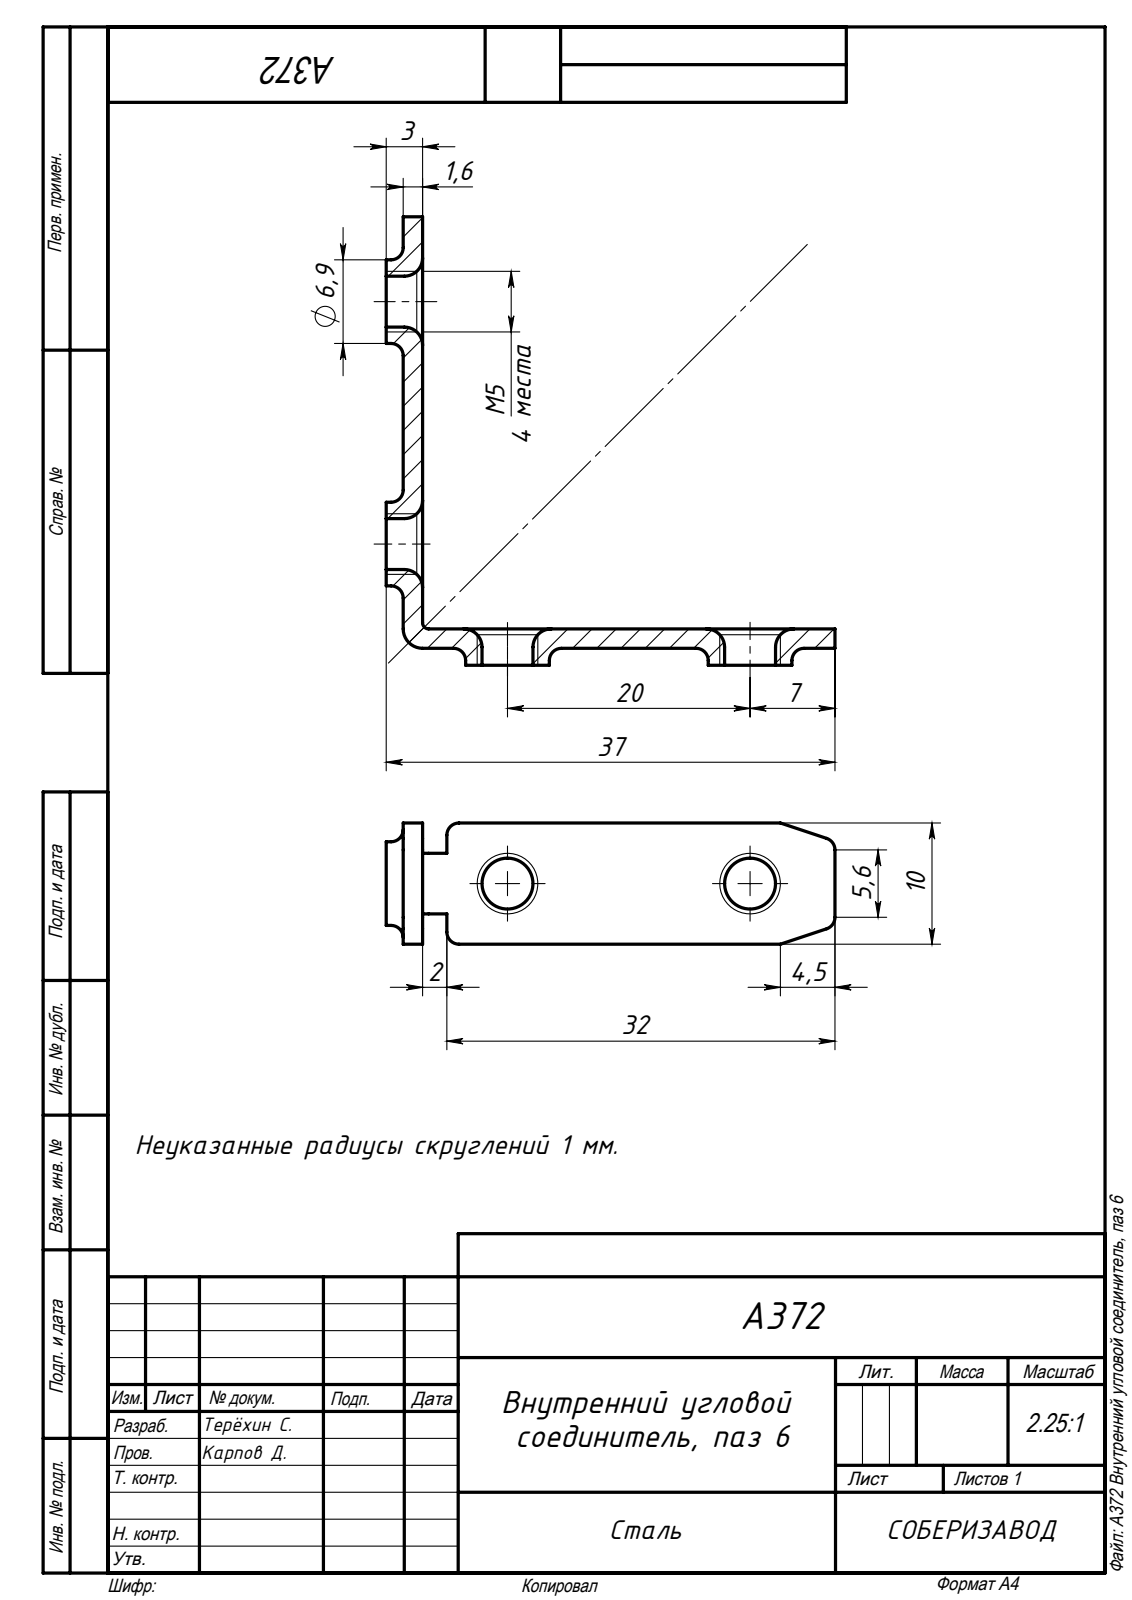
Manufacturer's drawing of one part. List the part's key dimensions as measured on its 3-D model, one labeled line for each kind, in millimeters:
Part name (STEP PRODUCT): A372 Внутренний угловой соединитель, паз 6
STEP written by: SolidWorks 2020 (AUTOMOTIVE_DESIGN)
Units: millimetres
Bodies: 1 solid, 66 faces (24 planar, 26 cylindrical, 16 other)
Overall size (bounding box): 37 × 37 × 10
Volume: 1 076 mm³ · Surface area: 1 663 mm²
Round holes (diameter × count): ⌀4.2 ×4
Round bosses / shafts (diameter × count): ⌀6.9 ×4
Partial cylindrical surfaces — rounded edges, fillets, slot ends (radius × count): R1 ×8, R0.5 ×1, R1.6 ×1
Main face-to-face distances: 1.6, 1.4, 3, 10, 5, 37, 35.6, 34, 2.5, 7.5
Hole centre spacings: 20
